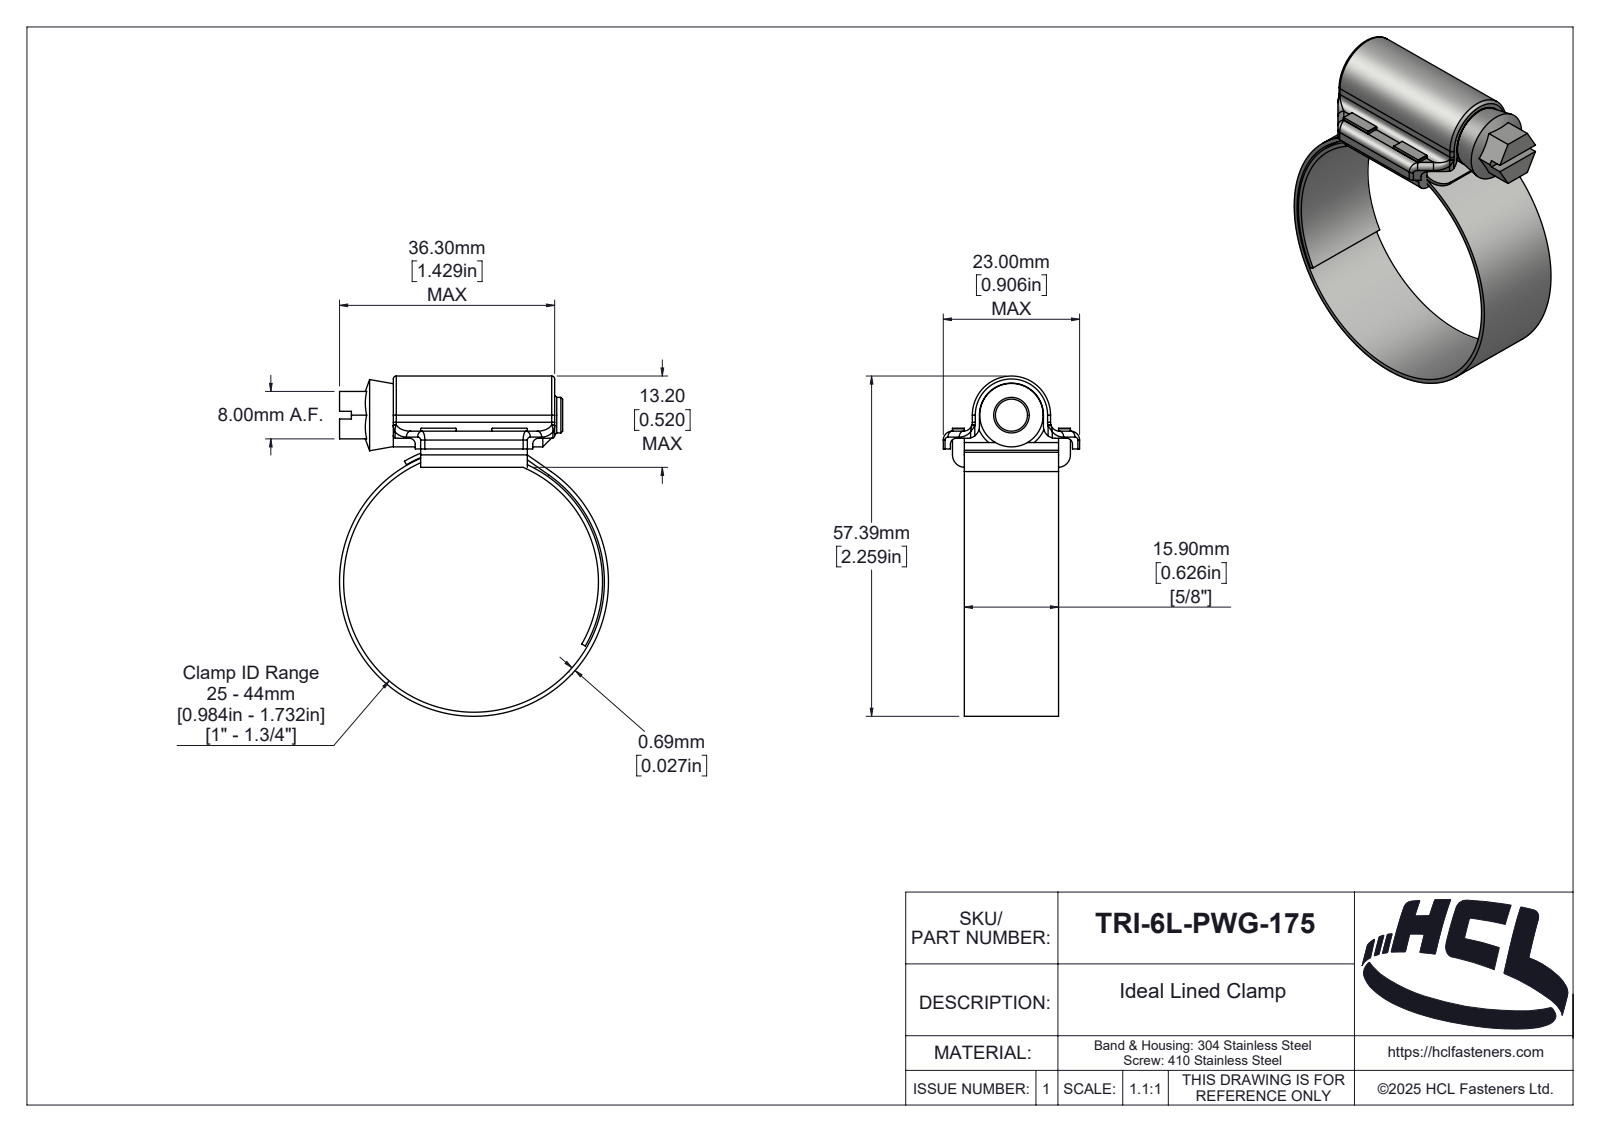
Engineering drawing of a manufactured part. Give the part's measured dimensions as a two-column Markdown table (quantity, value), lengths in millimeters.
| quantity | value |
| --- | --- |
| part name | TRI-6L-PWG-175 |
| STEP written by | SolidWorks 2025 (AUTOMOTIVE_DESIGN) |
| units | millimeters |
| bodies | 4 solids, 268 faces (87 planar, 102 cylindrical, 79 other) |
| overall size | 57.39 × 45.38 × 23 |
| volume | 7 363 mm³ |
| surface area | 11 168 mm² |
| round holes (diameter × count) | 44 × 1 |
| round bosses / shafts (diameter × count) | 45.38 × 1, 10.7 × 1, 6 × 1 |
| partial cylindrical surfaces (radius × count) | 1 × 14, 0.5 × 4, 1.5 × 4, 2 × 3, 0.1 × 2, 2.1 × 2, 3 × 2, 0.46 × 1 |
| main face-to-face distances | 2, 15.9, 17.9, 4.9, 1.2, 4.55, 3.35, 15.35, 2.55, 13.35 |
